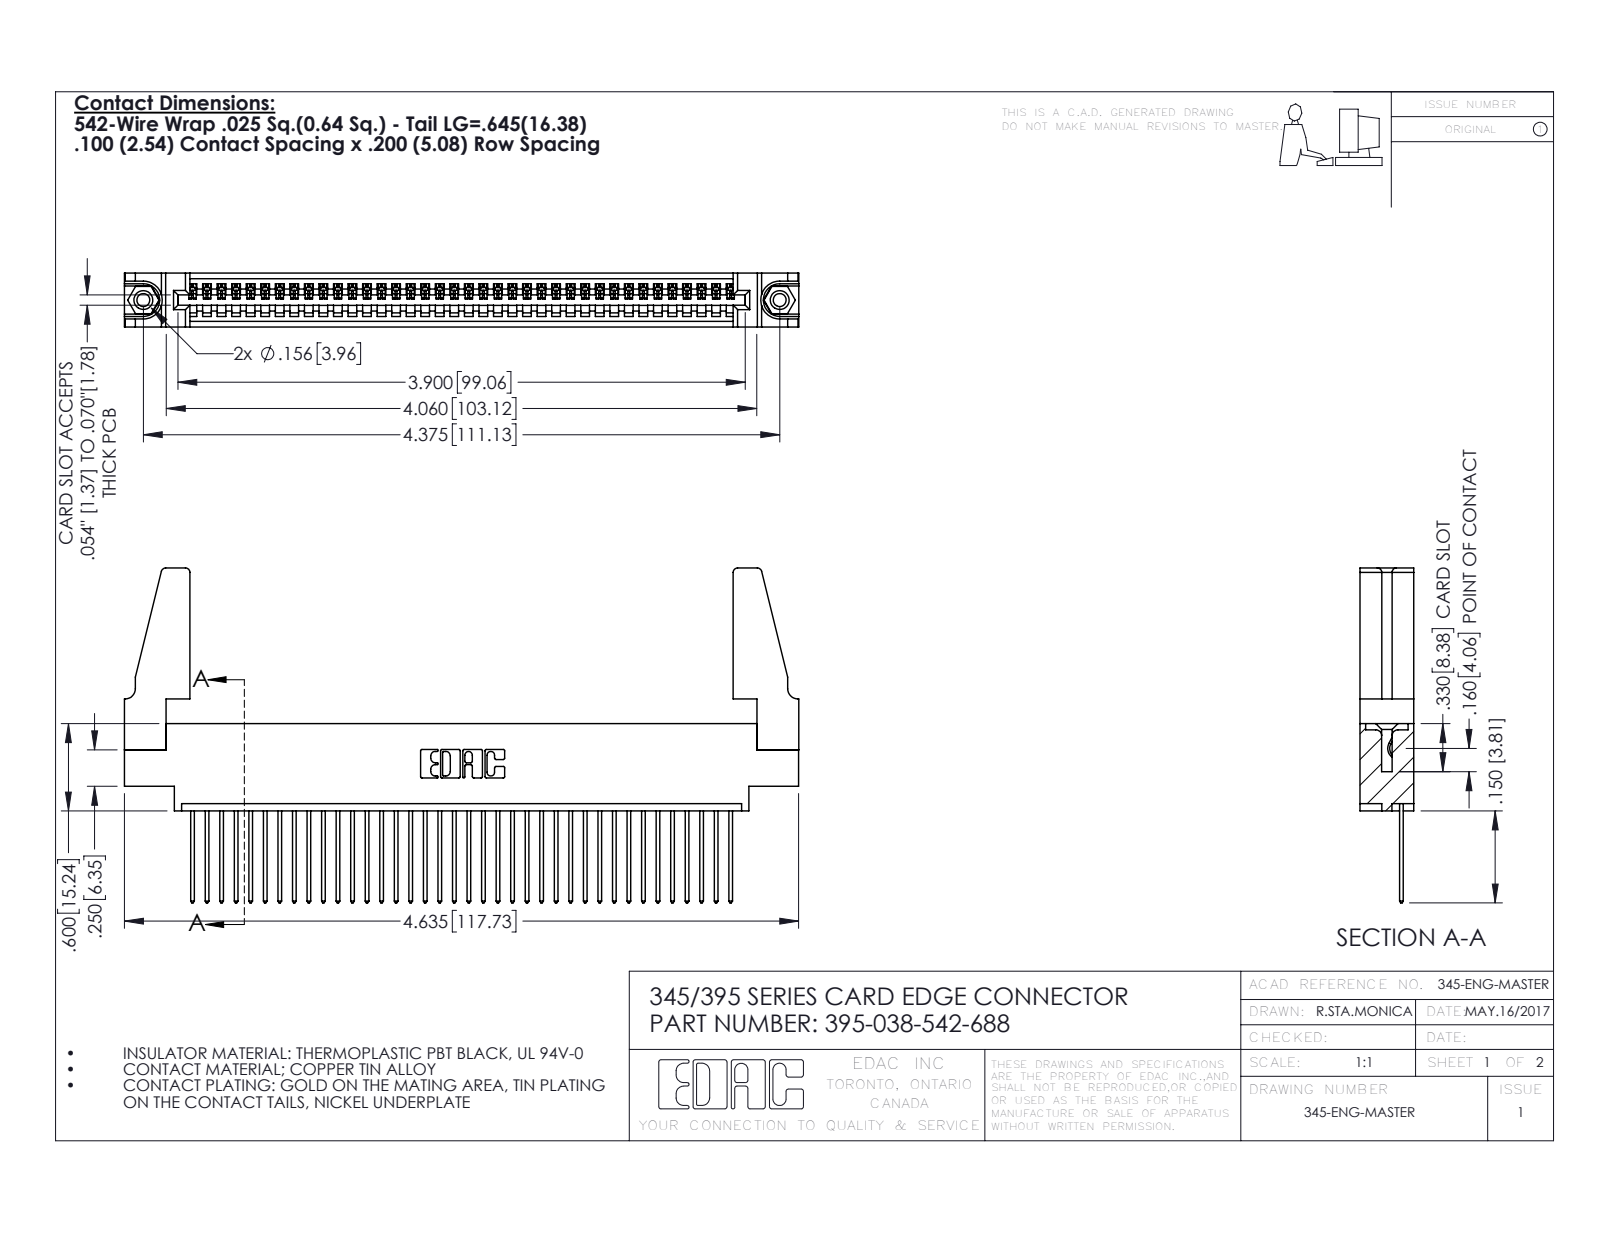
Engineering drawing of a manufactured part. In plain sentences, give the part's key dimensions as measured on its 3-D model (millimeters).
The part is named "395-038-542-688; 345 Part_0.170 Offset - 0.156 Dia-TH; 345-250-001_345-250-001-102; 345-220-078_345-220-088 (+1 more)". Its 3-D file was written by "SolidWorks 2016 (CONFIG_CONTROL_DESIGN)". It is 43 solids with 2458 faces: 1676 planar, 766 cylindrical and 16 other. Overall it measures 117.8 by 58.5 by 9.4 millimeters. Its volume is 14 400 cubic millimeters and its surface area 18 520 square millimeters. Round holes: 2 of diameter 2.3, 2 of diameter 3.2, 2 of diameter 4, 1 of diameter 1.6. Round bosses or shafts: 2 of diameter 3.9. Partial cylindrical surfaces (rounded edges, fillets, slot ends): 76 of radius 0.2, 76 of radius 0.3, 22 of radius 0.3, 8 of radius 0.8, 6 of radius 0.2, 6 of radius 0.8, 3 of radius 0.7, 2 of radius 0.8. The main face-to-face distances are 1.8, 7.6, 9.4, 2.5, 6.9, 0.6, 5.1, 5.7, 4.4, 3.8. The hole center spacings are 6.9, 105.1, 111.1.
